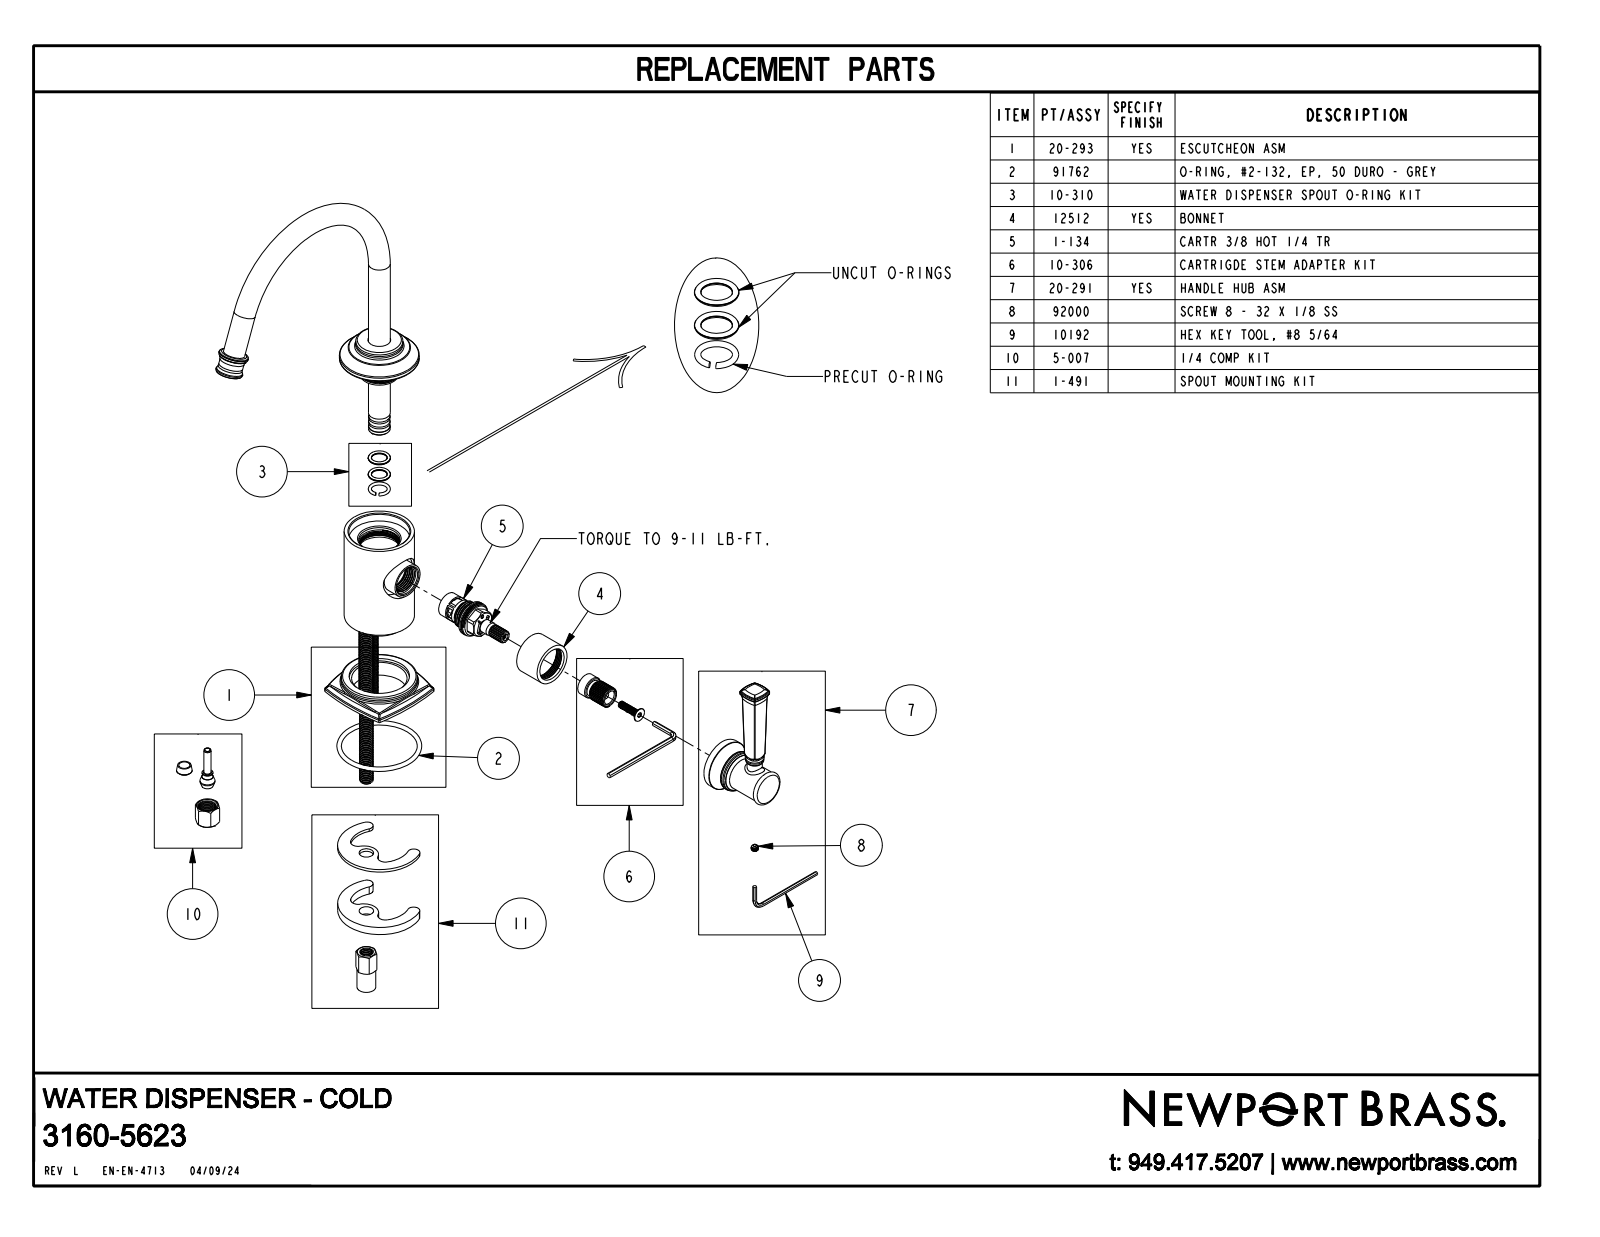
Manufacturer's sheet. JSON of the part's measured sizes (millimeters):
{"part_name": "3160-5623", "step_written_by": "CREO PARAMETRIC BY PTC INC, 2018400 (CONFIG_CONTROL_DESIGN)", "units": "millimeters", "bodies": {"solids": 1, "faces": 261, "planar": 11, "cylindrical": 38, "other": 212}, "overall_size": [238.1, 152.2, 89.7], "volume_mm3": 172700, "surface_area_mm2": 32940, "round_holes": [[25.4, 1]], "round_bosses_or_shafts": [[12.7, 2], [46.5, 1], [40.9, 1], [30.2, 1], [24.6, 1], [19.3, 1], [8.9, 1]], "partial_cylinders_radius": [[0.5, 4], [0.8, 4], [20.3, 4], [131.6, 4], [133.4, 4]], "face_to_face_distances": [82.7, 69.2, 13.5, 37.8, 10.8, 58.4, 71.9, 110.8, 100.1, 41.7]}
